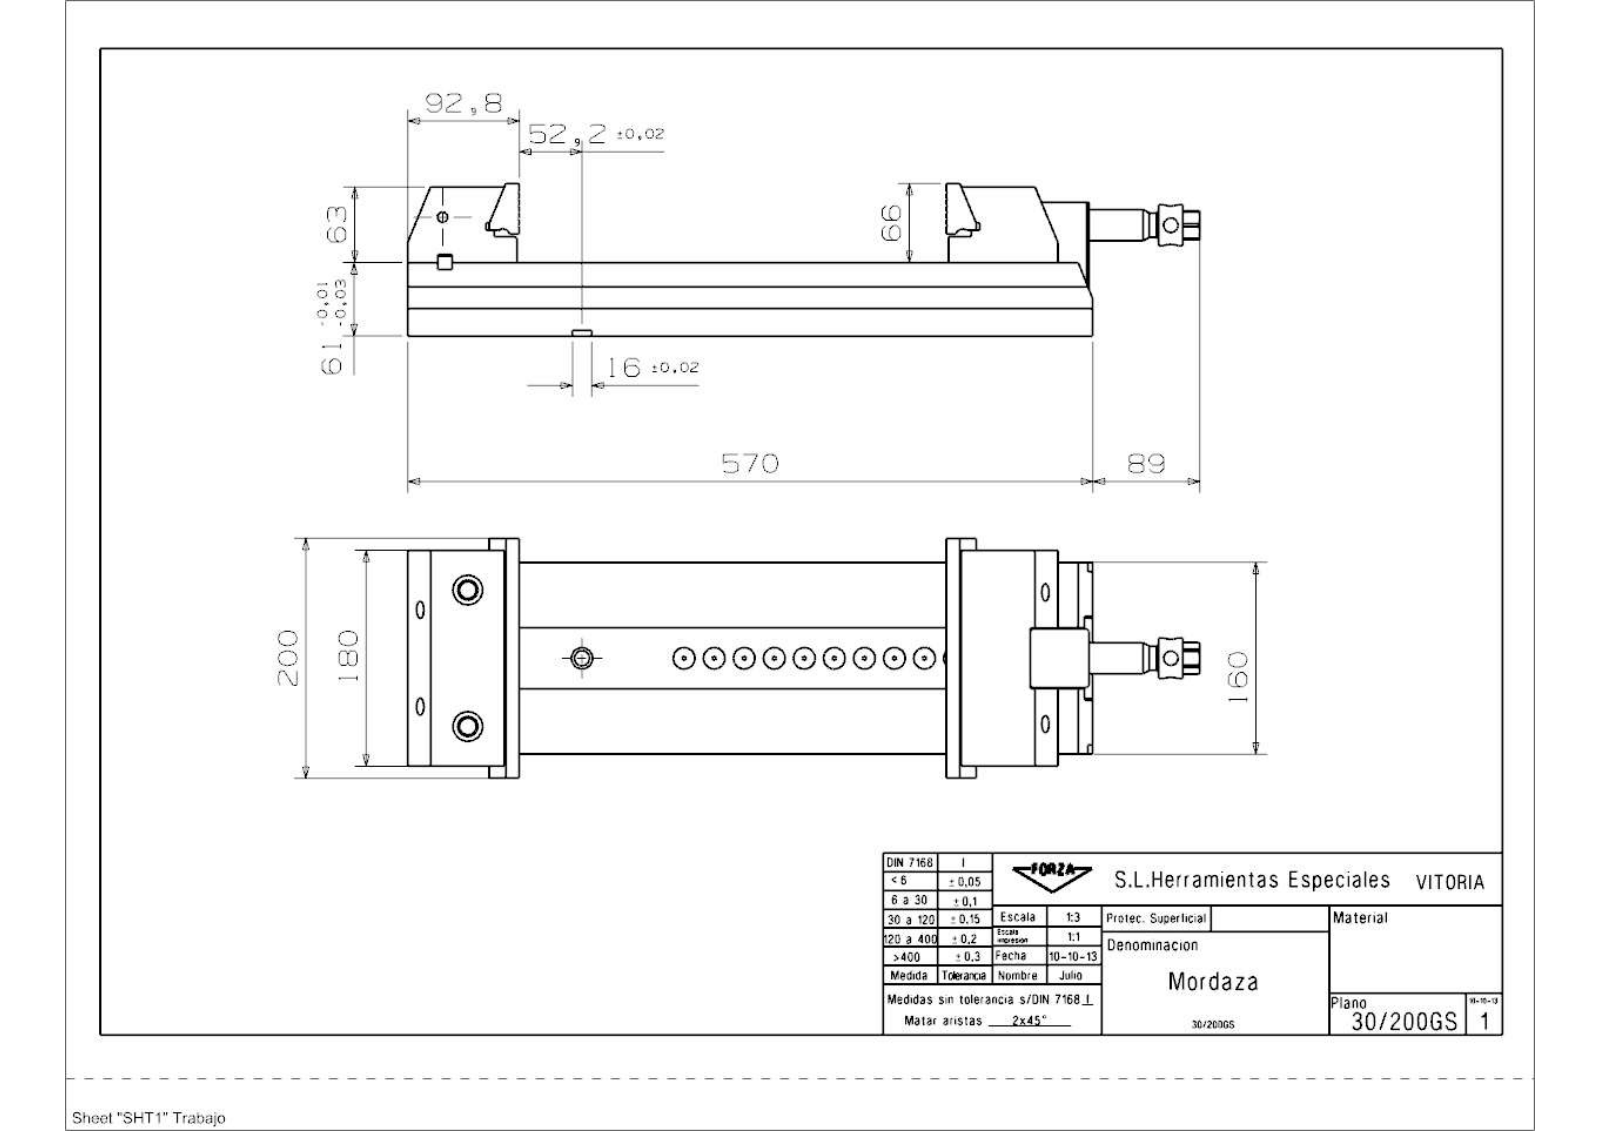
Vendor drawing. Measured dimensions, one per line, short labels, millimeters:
name: 30150070 Montaje Taco Hus; 30_200GS_Mordaza
written by: SIEMENS PLM Software NX 7.5 (CONFIG_CONTROL_DESIGN)
unit: mm
bodies: 12 solids, 497 faces (288 planar, 136 cylindrical, 73 other)
size: 659 × 200 × 126.95
volume: 6 237 000 mm³; area: 651 647 mm²
holes: 6× ⌀15, 5× ⌀5.19, 5× ⌀13, 4× ⌀6.99, 4× ⌀8.5, 4× ⌀10, 4× ⌀14.38, 3× ⌀8.78, 3× ⌀19, 2× ⌀12, 2× ⌀12.38, 2× ⌀17
bosses: 1× ⌀34, 1× ⌀33.8, 1× ⌀26, 1× ⌀20, 1× ⌀16.5
rounds: 24× R0.4, 4× R1.5, 4× R8, 4× R20, 2× R1.6, 2× R6, 2× R7, 1× R4
face distances: 61, 29.2, 31.8, 7.5, 160, 2, 27.2, 59, 124, 122
hole spacings: 14.5, 95.5, 81, 110, 16.47, 16.55, 24.08, 30
